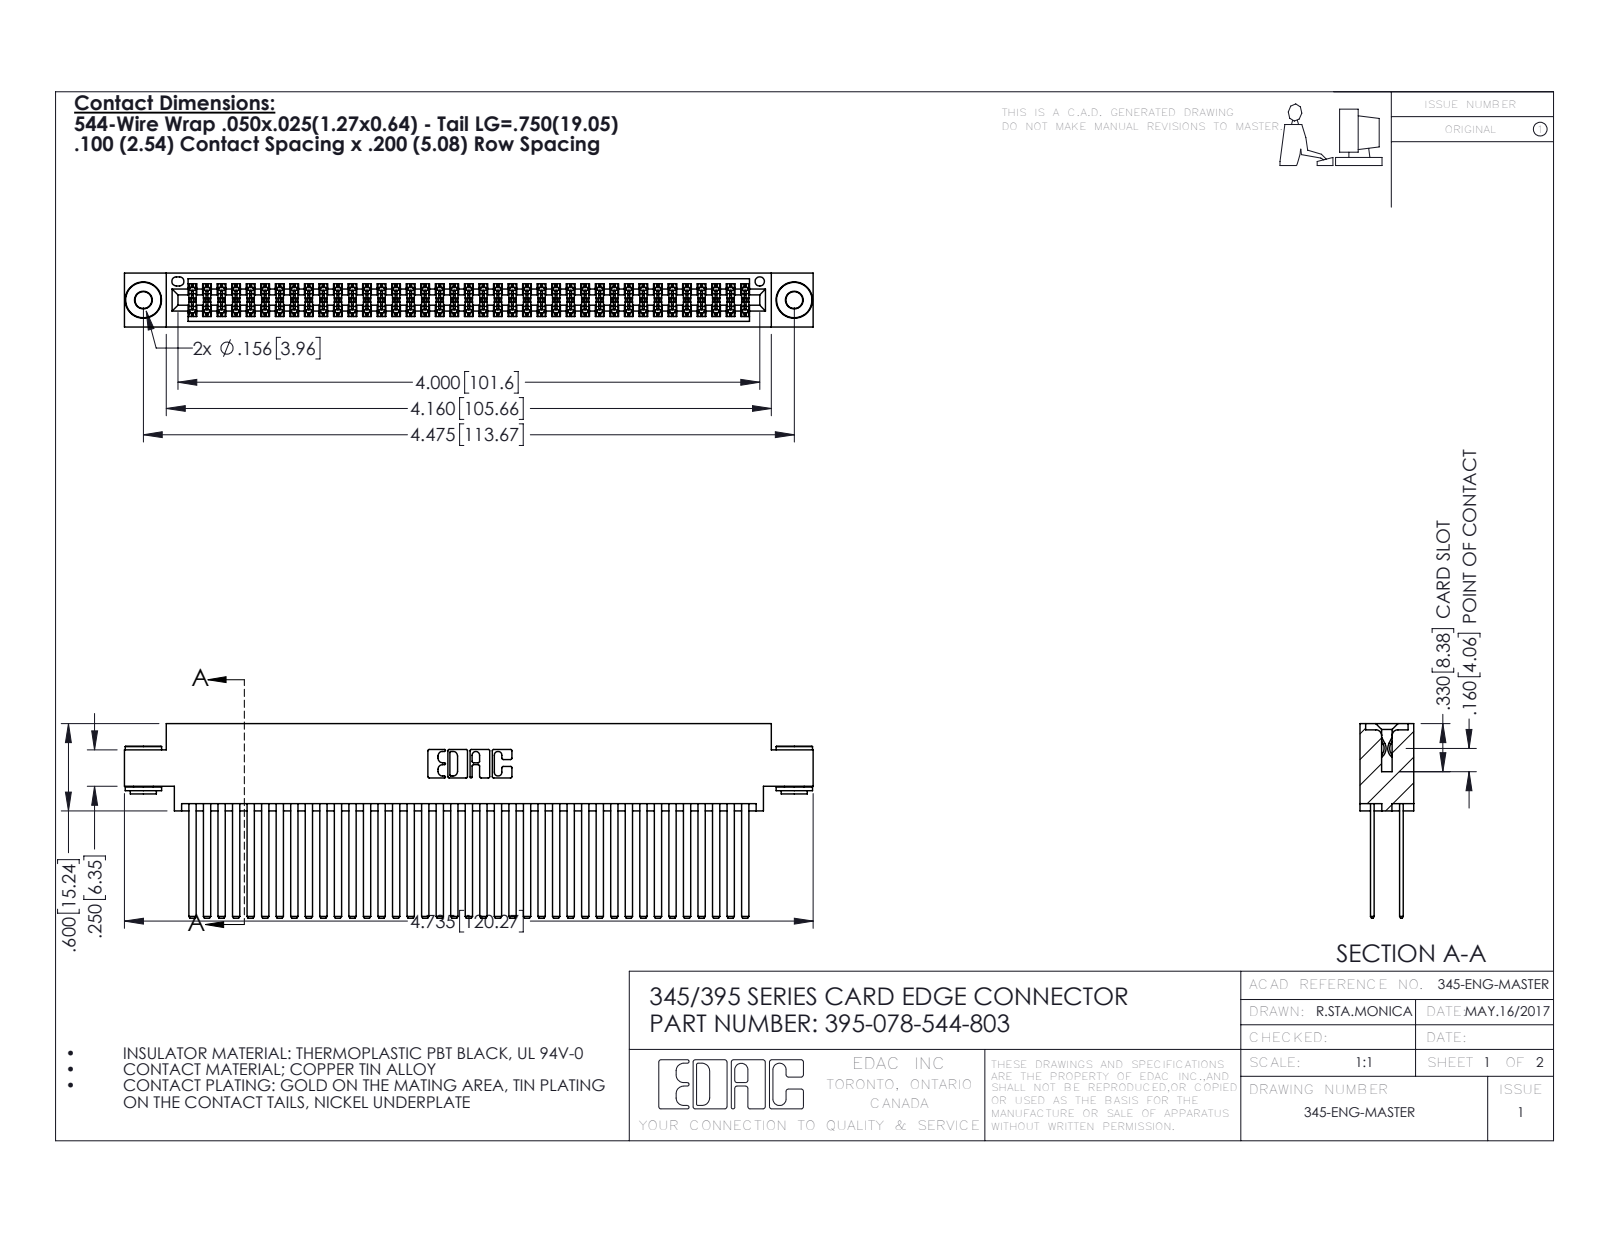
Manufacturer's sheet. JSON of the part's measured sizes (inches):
{"part_name": "345-292-001_345-293-144; 395-078-544-803; 345-250-002_345-250-002-102; 345 Part_0.170 Offset - 0.156 Dia-TH", "step_written_by": "SolidWorks 2016 (CONFIG_CONTROL_DESIGN)", "units": "inches", "bodies": {"solids": 81, "faces": 3600, "planar": 2356, "cylindrical": 1236, "other": 8}, "overall_size": [4.735, 1.337, 0.37], "volume_in3": 0.772, "surface_area_in2": 34.41, "round_holes": [[0.116, 2], [0.156, 2], [0.064, 1]], "round_bosses_or_shafts": [[0.25, 2], [0.18, 2], [0.136, 2]], "partial_cylinders_radius": [[0.006, 117], [0.01, 22], [0.007, 6], [0.031, 6], [0.026, 3], [0.014, 2], [0.019, 2], [0.022, 2]], "face_to_face_distances": [0.2, 0.025, 0.072, 0.098, 0.272, 0.298, 0.225, 0.175, 0.37, 0.15], "hole_center_spacings": [0.27, 4.239, 4.475]}
